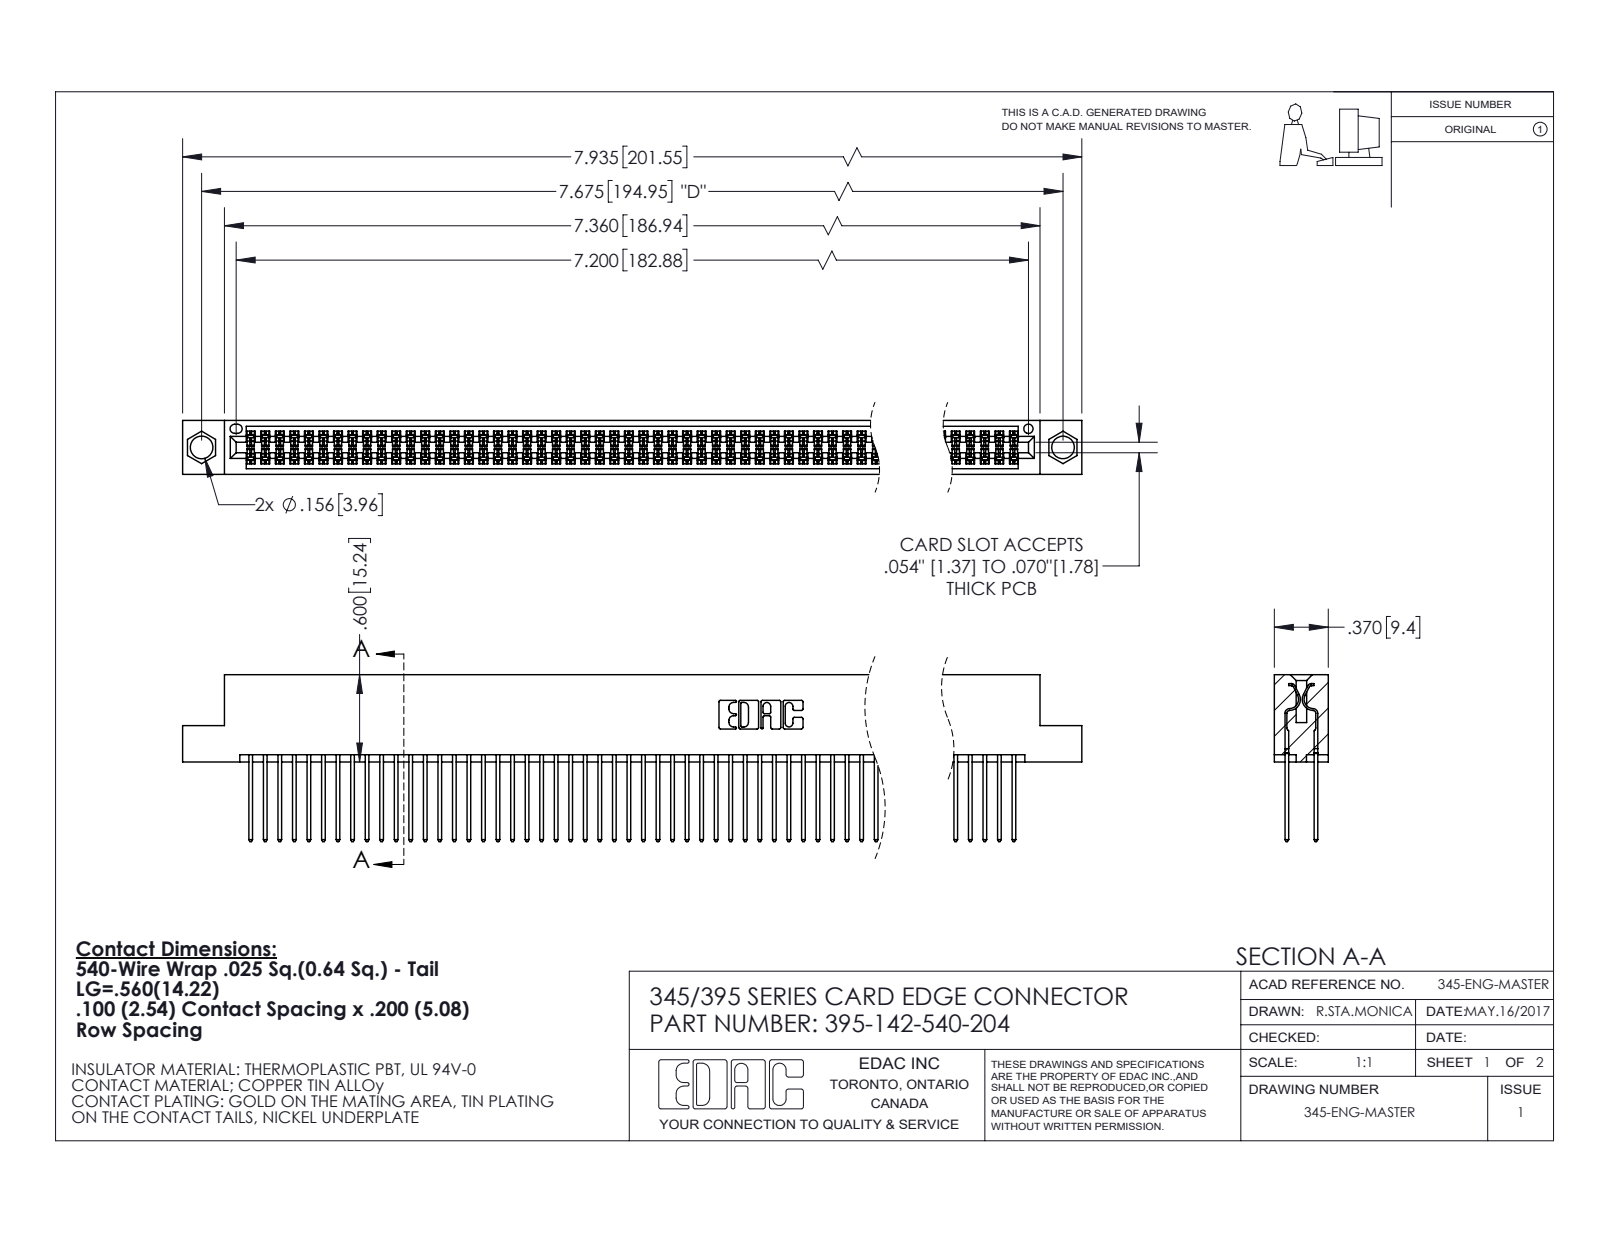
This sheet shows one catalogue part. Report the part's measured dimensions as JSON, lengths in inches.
{"part_name": "345 Part_Flush Mounting Lugs - 0.156 Dia-TI; 345-292-001_345-293-140; 395-142-540-204", "step_written_by": "SolidWorks 2020 (CONFIG_CONTROL_DESIGN)", "units": "inches", "bodies": {"solids": 143, "faces": 7240, "planar": 4780, "cylindrical": 2460, "other": 0}, "overall_size": [7.935, 1.147, 0.37], "volume_in3": 1.238, "surface_area_in2": 50.98, "round_holes": [[0.156, 2], [0.064, 1]], "partial_cylinders_radius": [[0.006, 213], [0.01, 142], [0.01, 22], [0.007, 6], [0.031, 6], [0.026, 3], [0.014, 2], [0.019, 2]], "face_to_face_distances": [0.298, 0.072, 0.2, 0.098, 0.272, 0.025, 0.225, 0.37, 0.175, 0.149], "hole_center_spacings": [0.27, 7.439, 7.675]}
